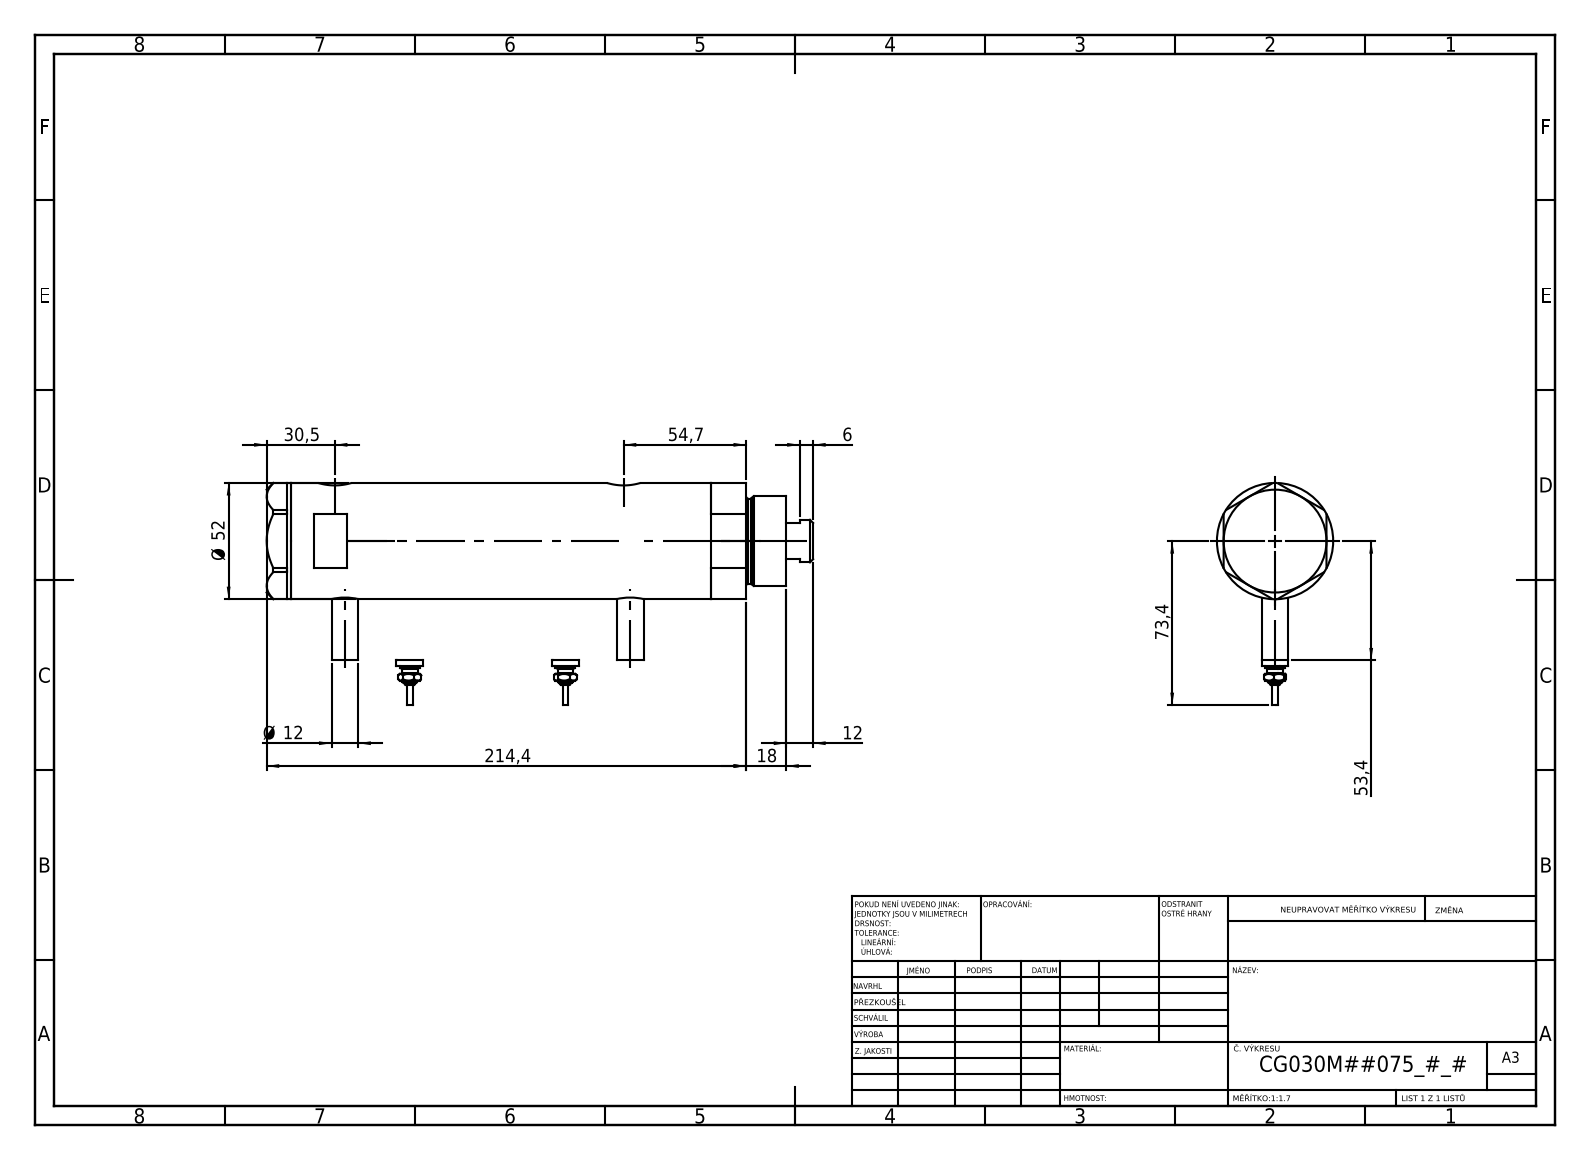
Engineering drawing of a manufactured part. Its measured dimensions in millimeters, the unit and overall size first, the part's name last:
Units: millimetres
Overall size (bounding box): 244.4 × 99.4 × 52
Round holes (diameter × count): ⌀9.73 ×2, ⌀12.5 ×2, ⌀15 ×2, ⌀6.5 ×1, ⌀20 ×1, ⌀21.5 ×1, ⌀30 ×1, ⌀33 ×1, ⌀44 ×1
Round bosses / shafts (diameter × count): ⌀12 ×4, ⌀9 ×2, ⌀7 ×2, ⌀4.5 ×2, ⌀2.5 ×2, ⌀52 ×1, ⌀40 ×1, ⌀38 ×1
Main face-to-face distances: 151.5, 23.8, 127.7, 11, 34.8, 162.5, 46, 36.4, 198.9, 187.9
Hole centre spacings: 2.9, 4.5, 124.7, 127.6, 129.2, 132.1
Volume: 450 686 mm³ · Surface area: 99 611 mm²
Bodies: 6 solids, 226 faces (93 planar, 69 cylindrical, 64 other)
Part name (STEP PRODUCT): V270CG_MIDDLE; V270CG_VC; Switch; V270CG_FRONT (+1 more)
STEP written by: SolidWorks 2019 (CONFIG_CONTROL_DESIGN)
